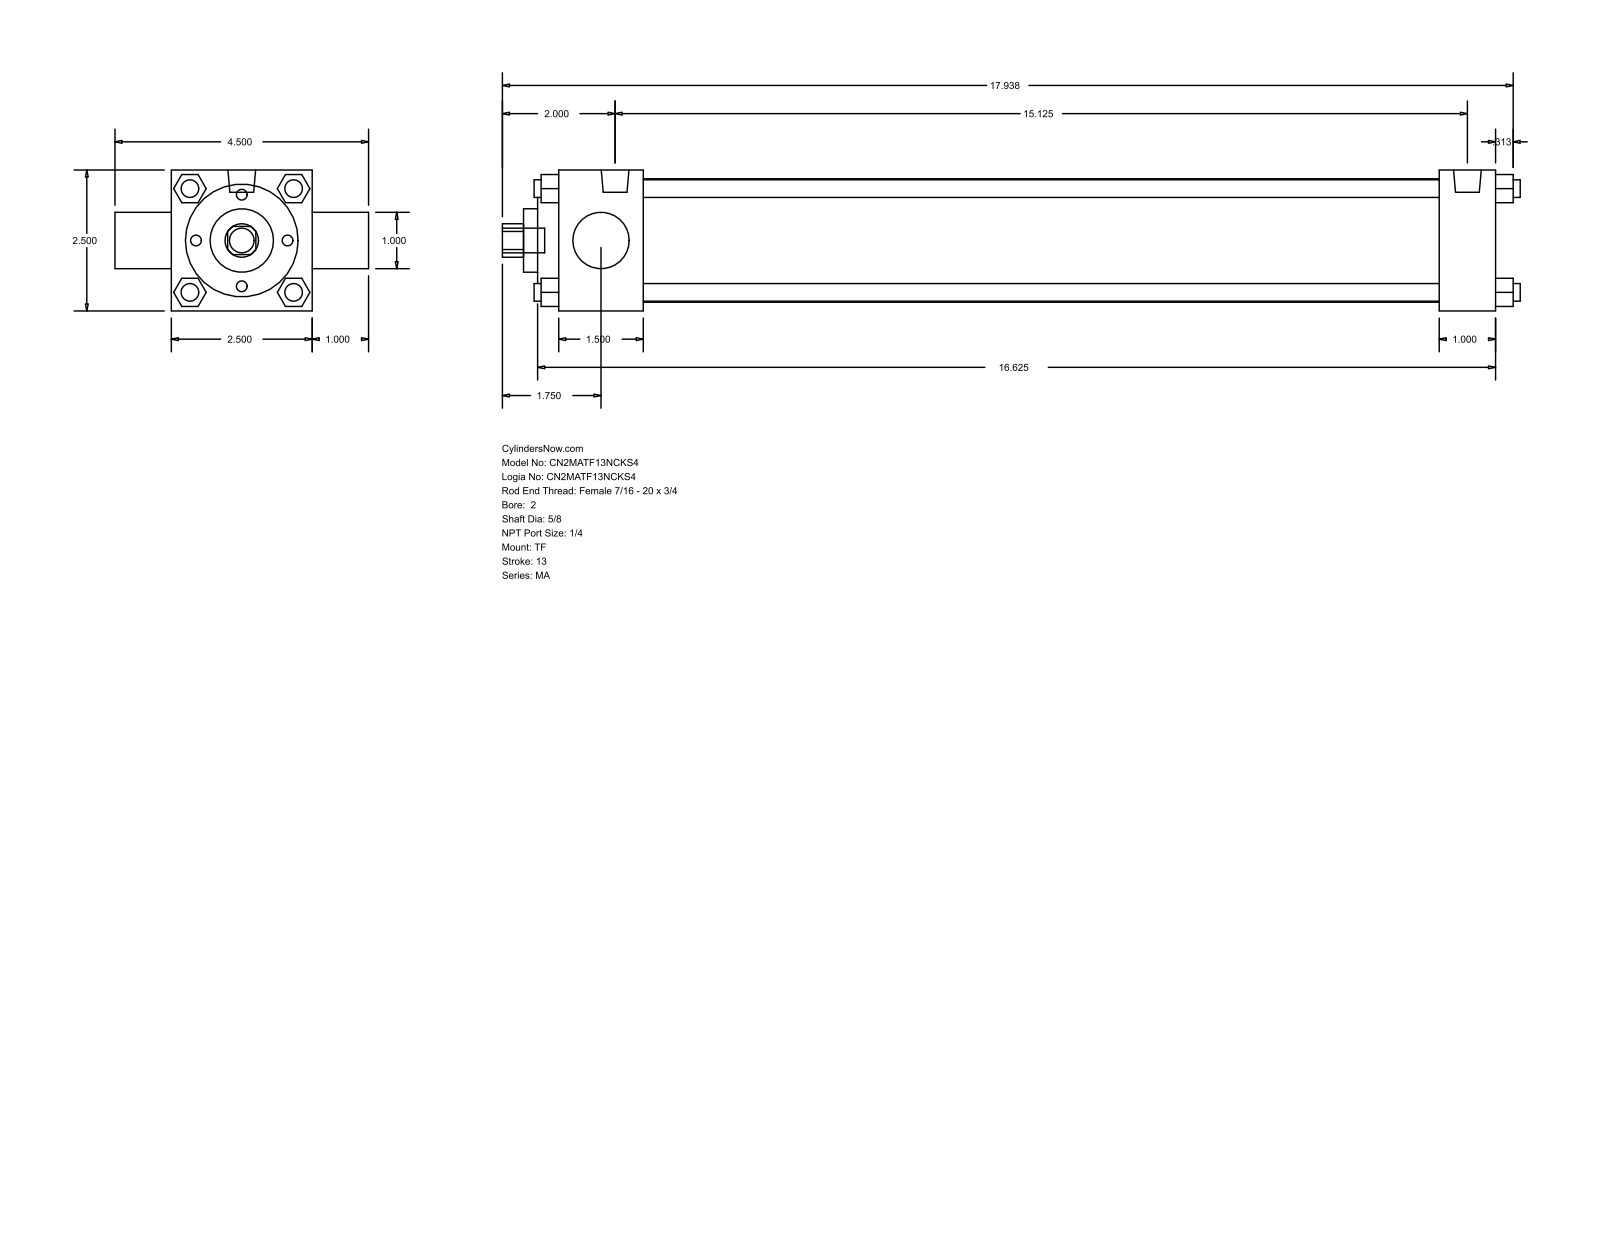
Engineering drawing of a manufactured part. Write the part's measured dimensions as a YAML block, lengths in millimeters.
part_name: "MA_TF__0200_0.625"
step_written_by: "GSSL Pune (CONFIG_CONTROL_DESIGN)"
units: millimeters
bodies: {solids: 0, faces: 122, planar: 93, cylindrical: 29, other: 0}
overall_size: [458.79, 114.3, 63.5]
round_holes:
  - {diameter: 15.88, count: 1}
  - {diameter: 25.4, count: 1}
  - {diameter: 28.57, count: 1}
  - {diameter: 50.8, count: 1}
  - {diameter: 55.63, count: 1}
round_bosses_or_shafts:
  - {diameter: 7.94, count: 7}
  - {diameter: 12.49, count: 2}
  - {diameter: 11.11, count: 1}
partial_cylinders:
  - {radius: 7.54, count: 1}
face_to_face_distances: [63.5, 38.1, 12.7, 9.52, 422.28, 396.87, 358.77, 384.18, 25.41, 47.62]
